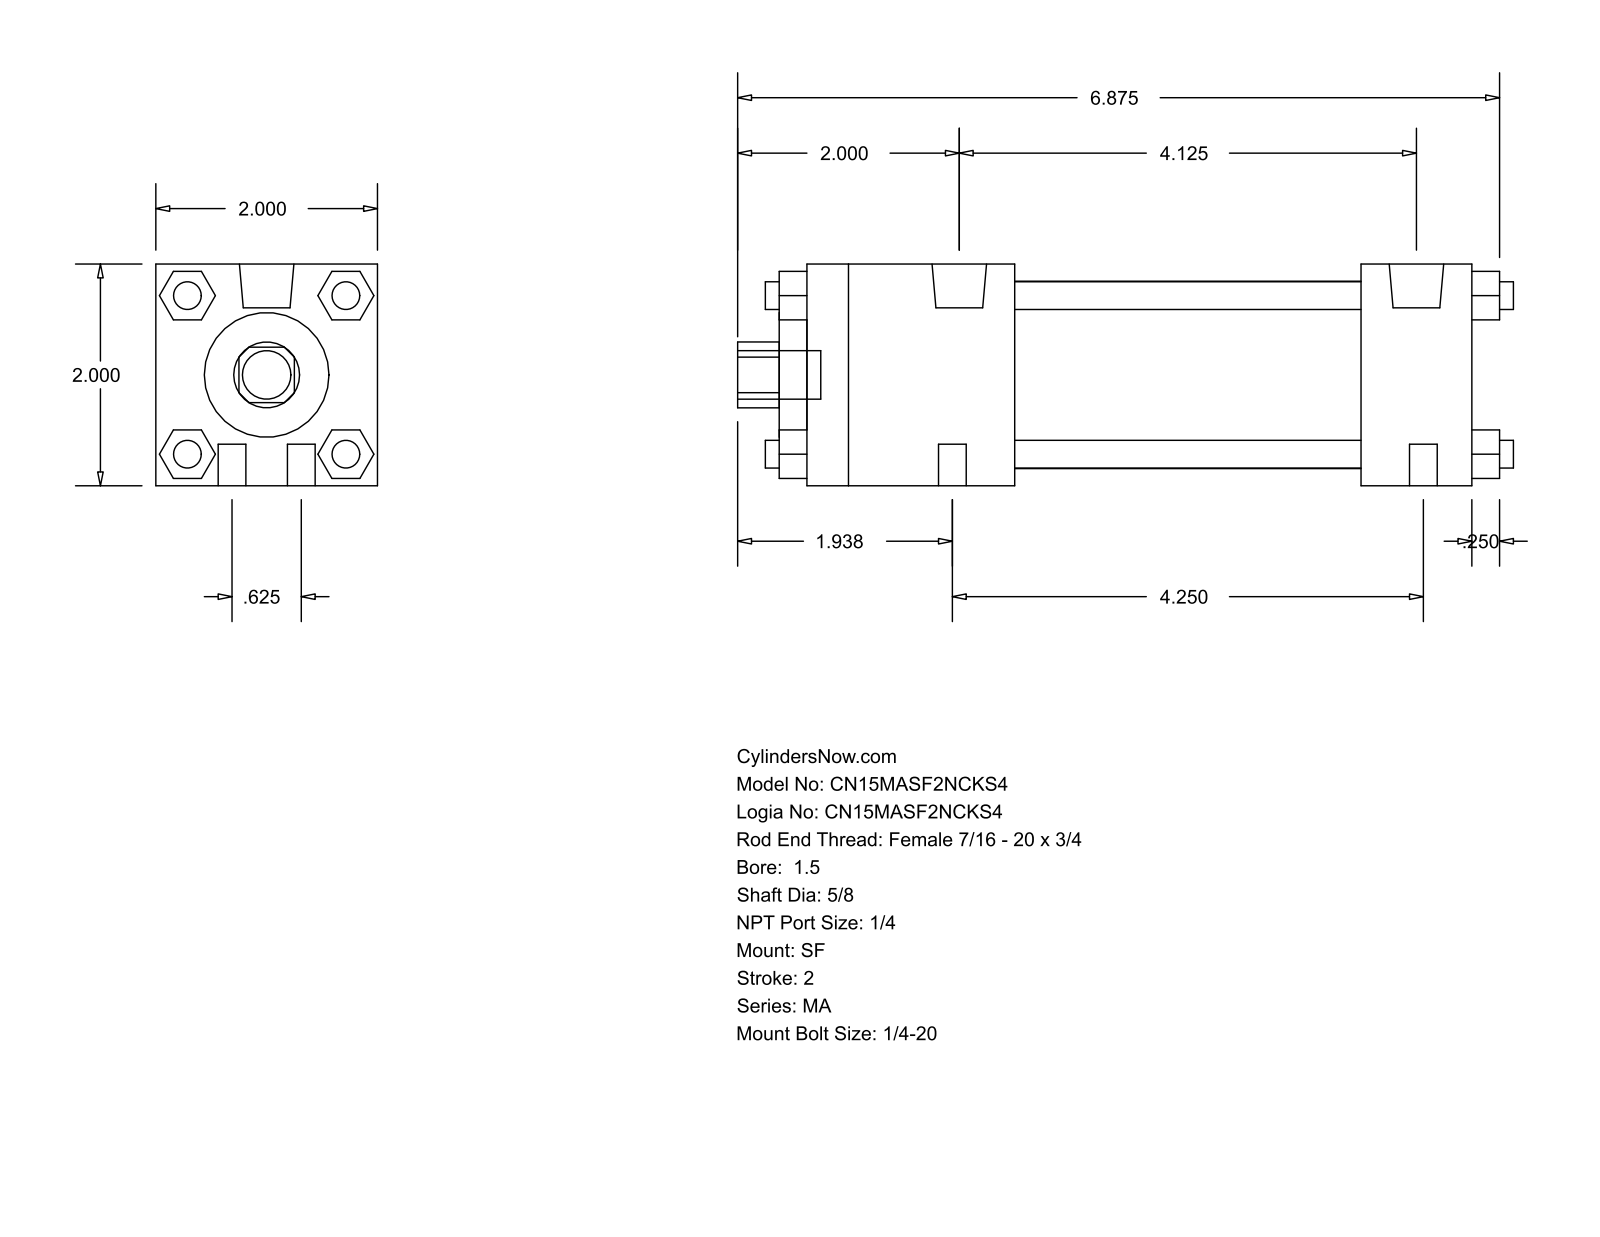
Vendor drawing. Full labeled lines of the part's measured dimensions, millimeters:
Part name (STEP PRODUCT): MA_SF__0150_0.625
STEP written by: GSSL Pune (CONFIG_CONTROL_DESIGN)
Units: millimetres
Bodies: 0 solids, 124 faces (94 planar, 30 cylindrical, 0 other)
Overall size (bounding box): 177.8 × 50.8 × 50.8
Round holes (diameter × count): ⌀15.88 ×1, ⌀28.57 ×1, ⌀42.93 ×1
Round bosses / shafts (diameter × count): ⌀6.35 ×8, ⌀12.49 ×2, ⌀7.94 ×2, ⌀11.11 ×1
Partial cylindrical surfaces — rounded edges, fillets, slot ends (radius × count): R7.54 ×1
Main face-to-face distances: 50.8, 152.4, 47.62, 127, 79.38, 104.78, 25.4, 6.35, 158.75, 53.97
